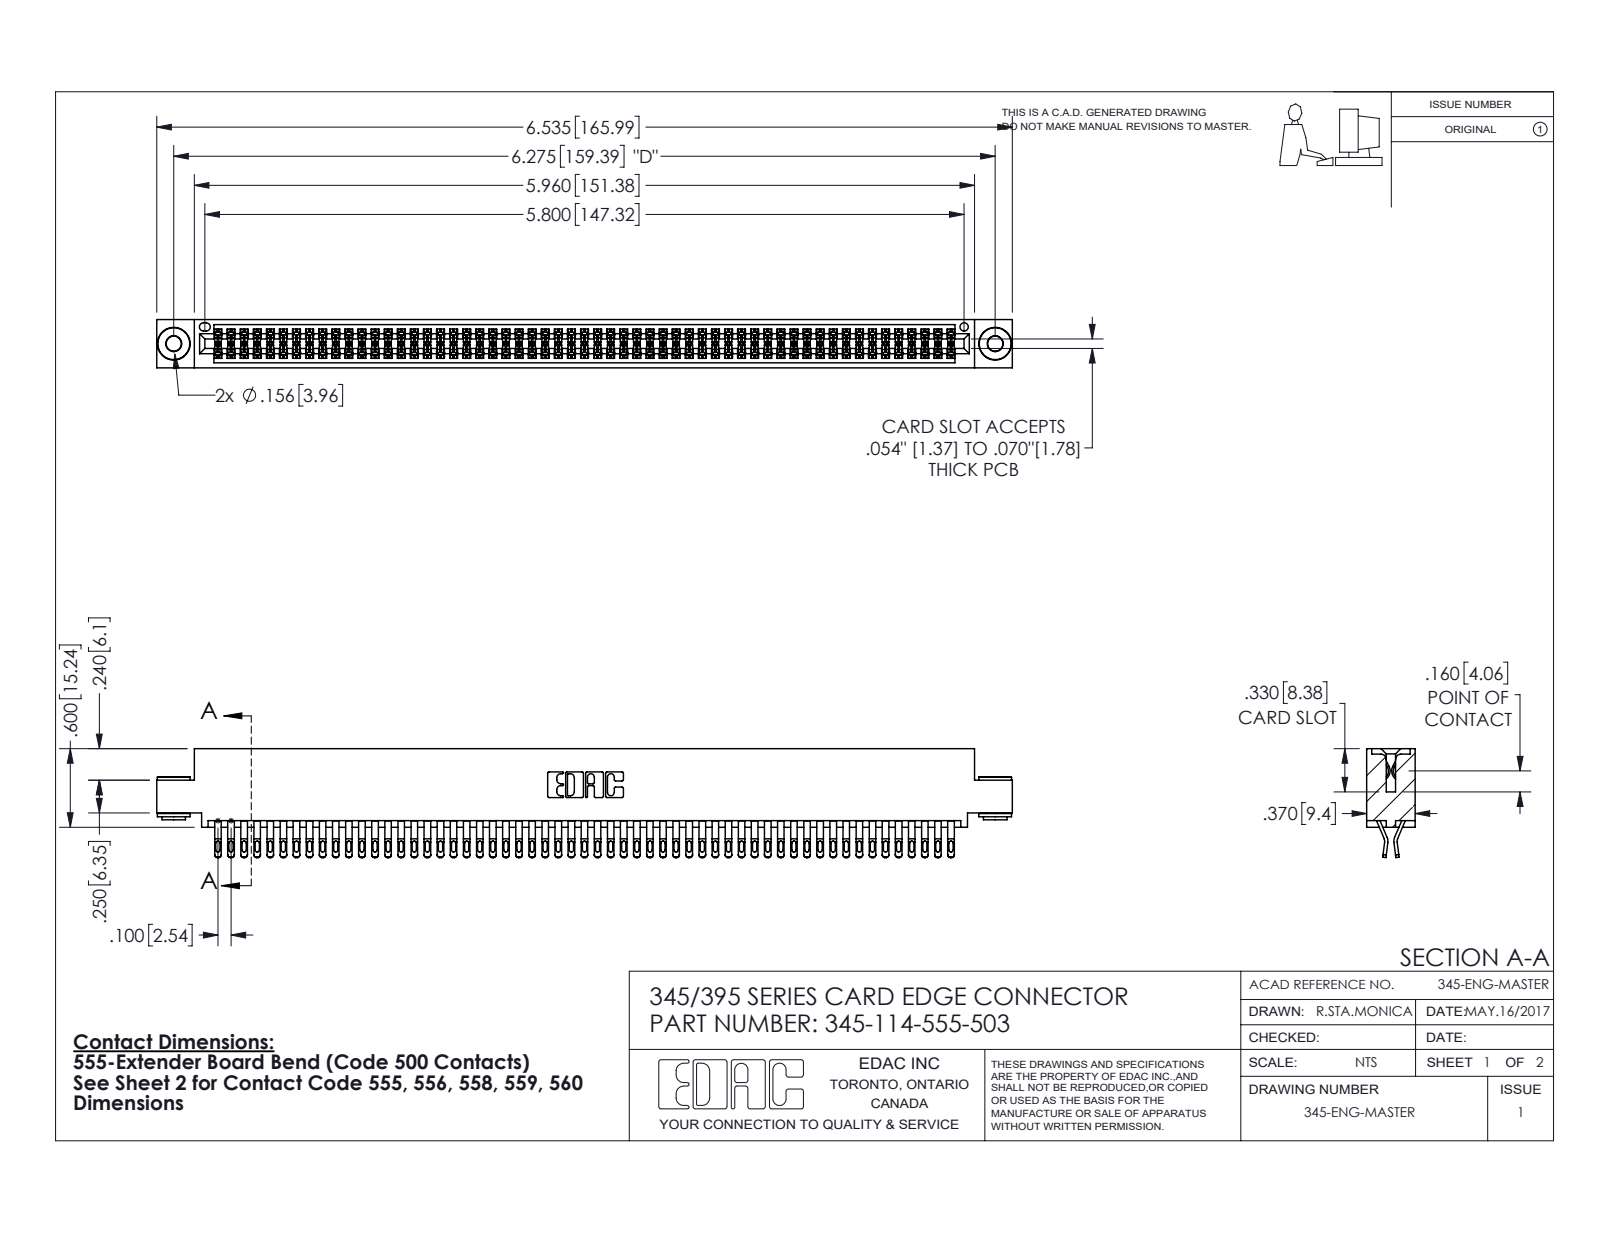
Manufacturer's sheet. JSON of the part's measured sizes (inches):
{"part_name": "345 Part_0.110 Offset - 0.156 Dia-TH; 345-250-002_345-250-002-102; 345-114-555-503; 345-292-001_555 Tail", "step_written_by": "SolidWorks 2016 (CONFIG_CONTROL_DESIGN)", "units": "inches", "bodies": {"solids": 117, "faces": 6552, "planar": 3628, "cylindrical": 2916, "other": 8}, "overall_size": [6.535, 0.832, 0.37], "volume_in3": 1.009, "surface_area_in2": 40.59, "round_holes": [[0.116, 2], [0.156, 2], [0.064, 1]], "round_bosses_or_shafts": [[0.25, 2], [0.18, 2], [0.136, 2]], "partial_cylinders_radius": [[0.016, 285], [0.02, 228], [0.006, 171], [0.01, 22], [0.007, 6], [0.031, 6], [0.026, 3], [0.01, 2]], "face_to_face_distances": [0.072, 0.298, 0.025, 0.37, 0.2, 0.098, 0.272, 0.225, 0.175, 0.149], "hole_center_spacings": [0.27, 6.039, 6.275]}
